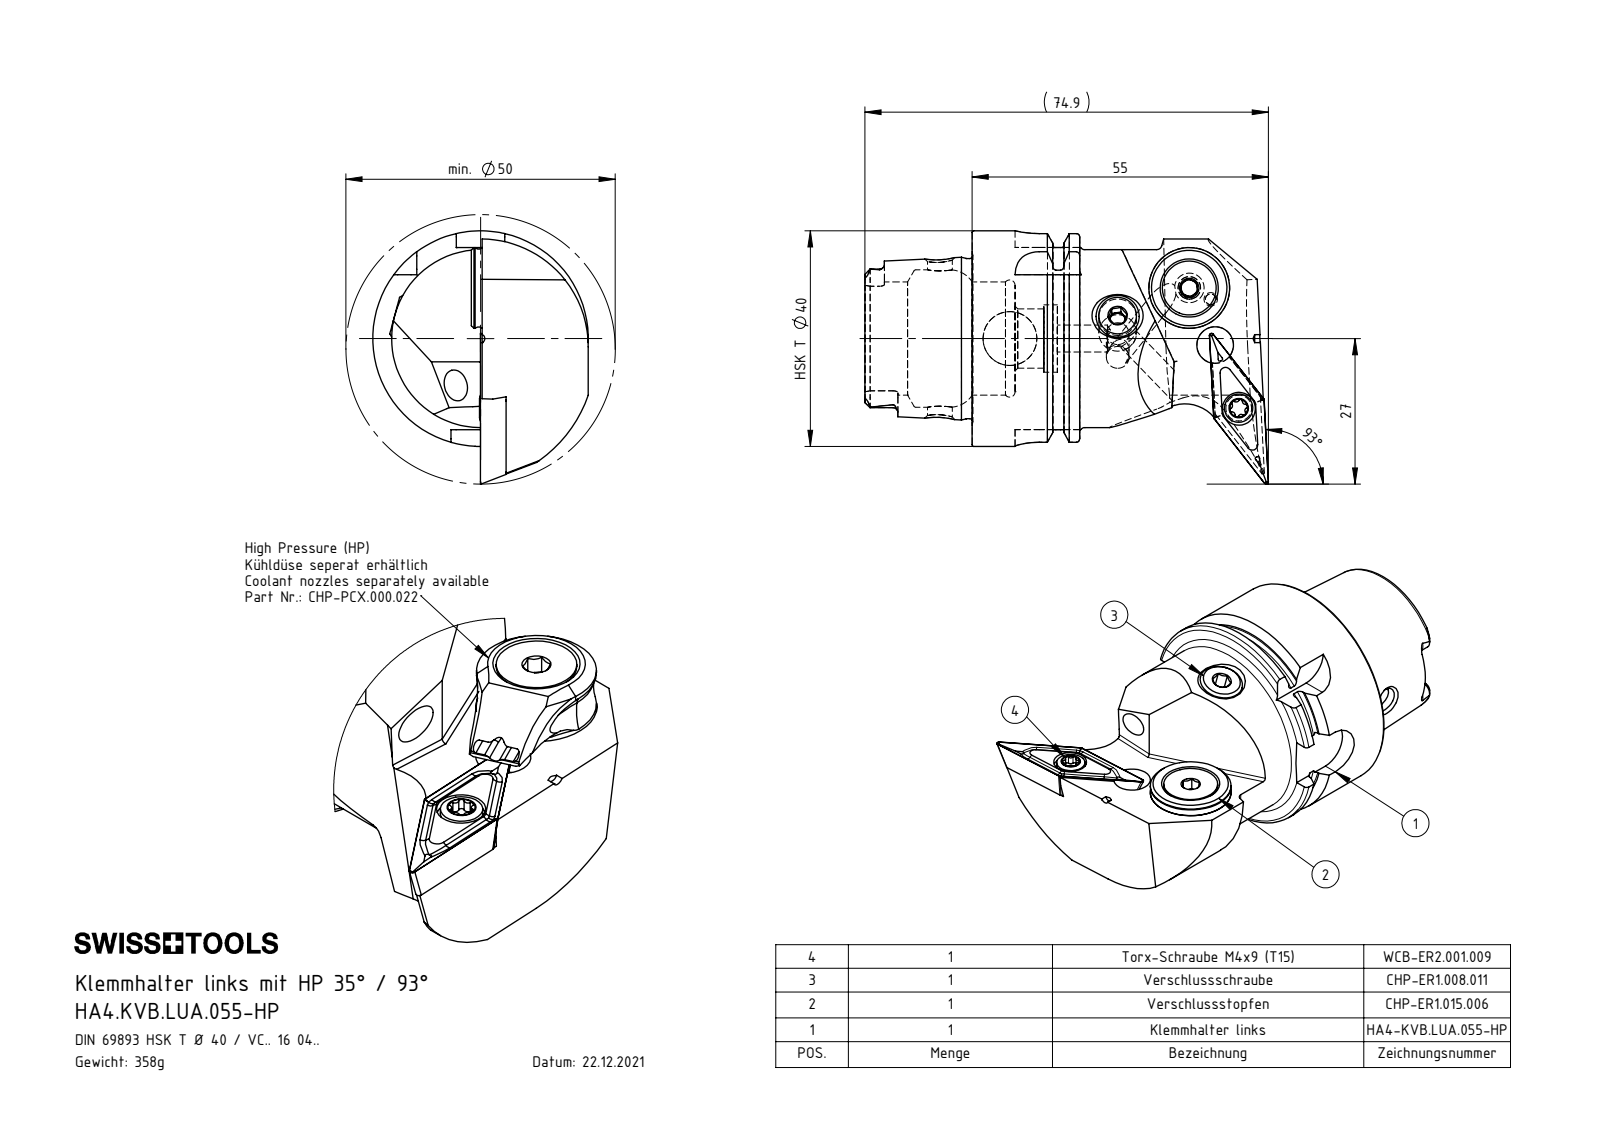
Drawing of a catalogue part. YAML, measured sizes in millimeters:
part_name: "ISO 8752 2x8; CHP-ER1.015.006_A; HA4.KVB.LUA.055-HP; CHP-ER1.015.006 (+6 more)"
step_written_by: "SolidWorks 2022 (AUTOMOTIVE_DESIGN)"
units: millimeters
bodies: {solids: 8, faces: 422, planar: 118, cylindrical: 120, other: 184}
overall_size: [74.9, 47, 40]
volume: 45045
surface_area: 16840
round_holes:
  - {diameter: 4.2, count: 4}
  - {diameter: 1.2, count: 1}
  - {diameter: 2, count: 1}
  - {diameter: 2.5, count: 1}
  - {diameter: 3, count: 1}
  - {diameter: 3.3, count: 1}
  - {diameter: 4.4, count: 1}
  - {diameter: 4.6, count: 1}
  - {diameter: 5, count: 1}
  - {diameter: 5.2, count: 1}
  - {diameter: 6.1, count: 1}
  - {diameter: 6.8, count: 1}
round_bosses_or_shafts:
  - {diameter: 40, count: 1}
  - {diameter: 34.75, count: 1}
  - {diameter: 33, count: 1}
  - {diameter: 29.71, count: 1}
  - {diameter: 15, count: 1}
  - {diameter: 13.4, count: 1}
  - {diameter: 10, count: 1}
  - {diameter: 8, count: 1}
partial_cylinders:
  - {radius: 0.34, count: 6}
  - {radius: 0.59, count: 6}
  - {radius: 0.9, count: 6}
  - {radius: 4.5, count: 4}
  - {radius: 0.5, count: 2}
  - {radius: 1.82, count: 2}
  - {radius: 1.88, count: 2}
  - {radius: 0.8, count: 1}
face_to_face_distances: [4.5, 4.46, 7.95, 19.95, 12, 15.2, 15.24, 19.7, 19.9, 27.85]
hole_center_spacings: [4.5, 8.51, 11.62, 12.5, 12.62, 20.84, 20.96, 24.11]
